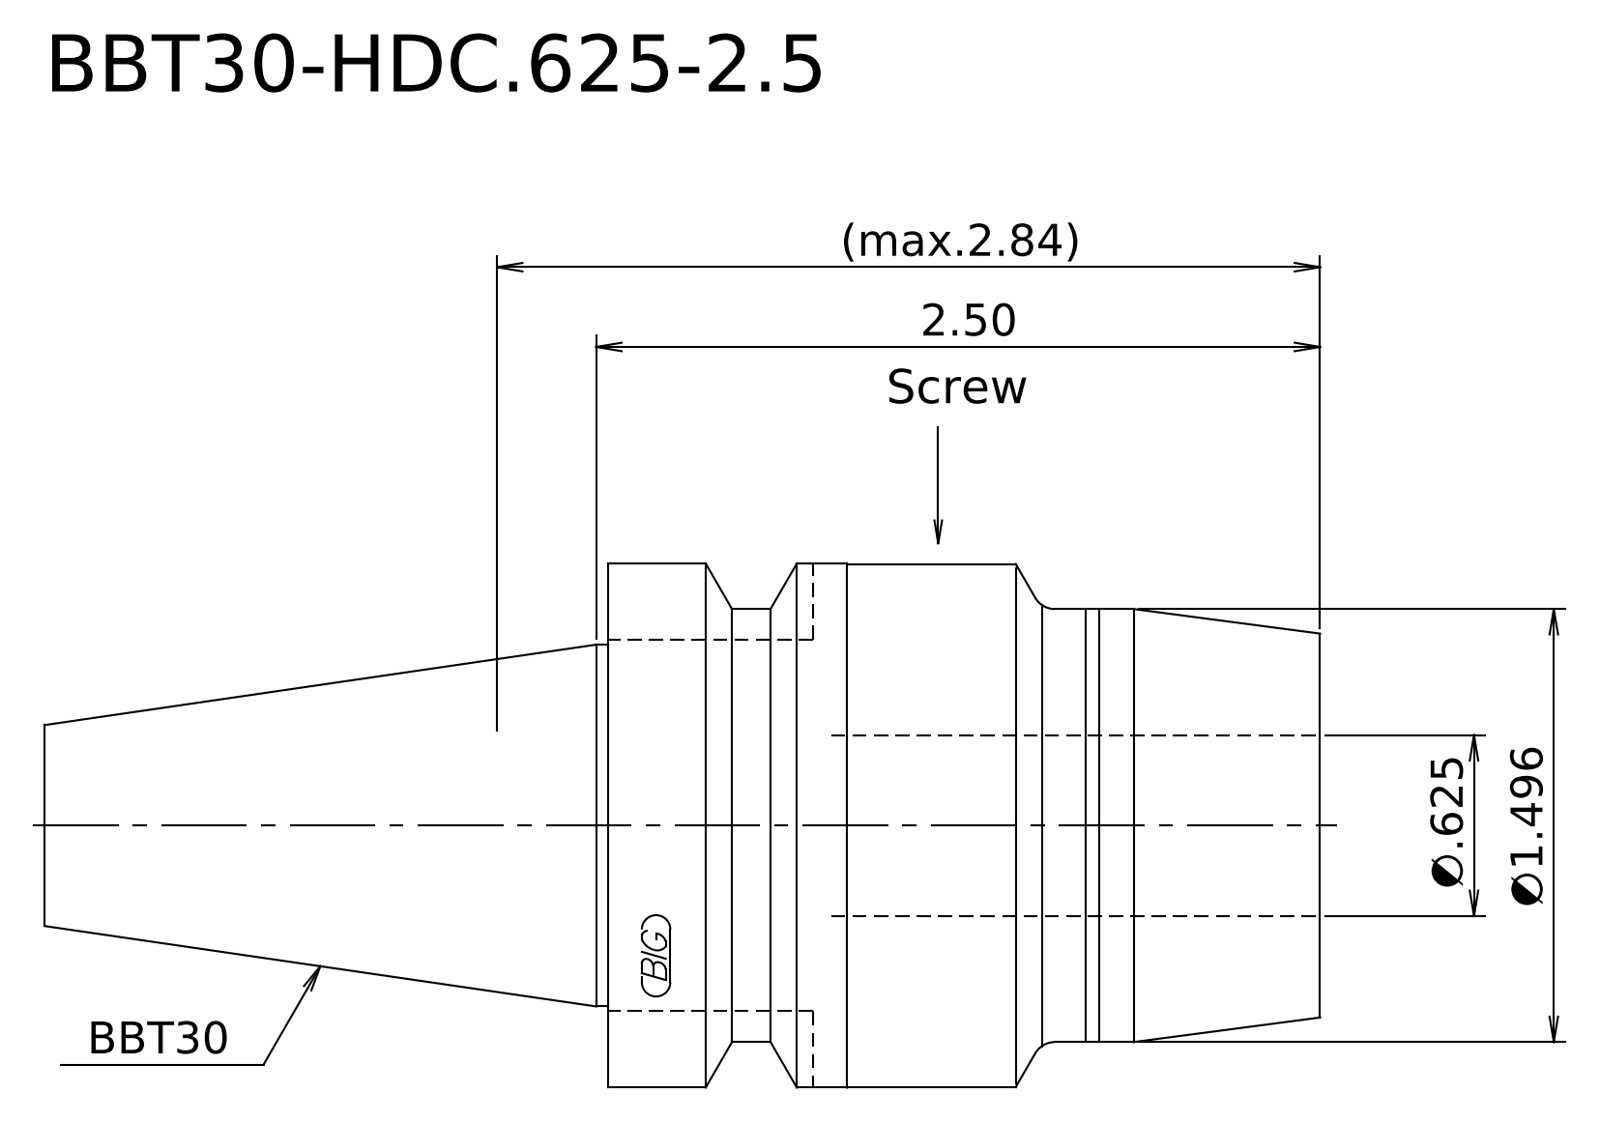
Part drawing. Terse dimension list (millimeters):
written by: Kubotek KeyCreator 2011 V10.0.2 (22737) (automotive_design)
unit: mm
bodies: 1 solid, 16 faces (3 planar, 6 cylindrical, 7 other)
size: 111.9 × 46 × 46
volume: 109 847 mm³; area: 14 925 mm²
bosses: 1× ⌀46, 1× ⌀45.9, 1× ⌀38, 1× ⌀31.75
face distances: 62.5, 111.9, 49.4
